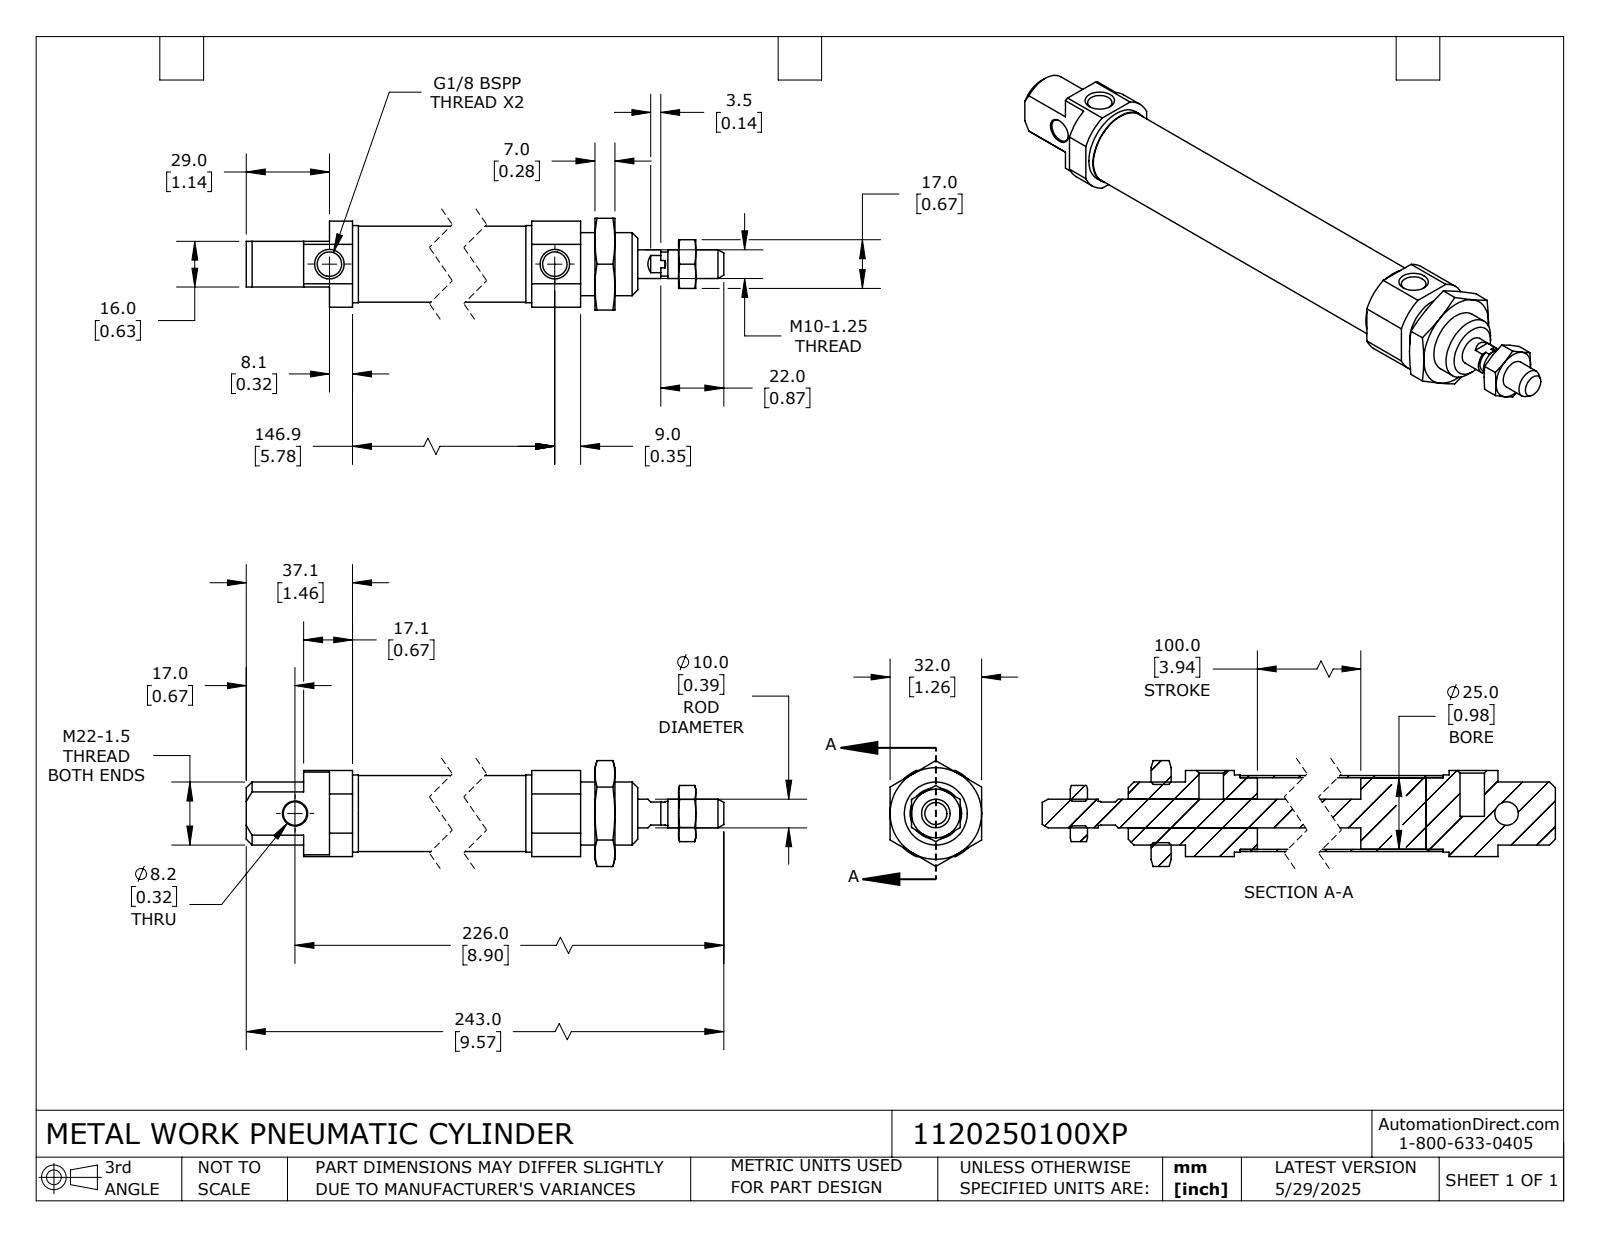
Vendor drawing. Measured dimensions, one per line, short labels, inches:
name: 1120250100XP; 1120250100XP_BODY; 1120250100XP_ROD
written by: SolidWorks 2024 (CONFIG_CONTROL_DESIGN)
unit: in
bodies: 6 solids, 144 faces (54 planar, 44 cylindrical, 46 other)
size: 9.567 × 1.455 × 1.26
volume: 4.798 in³; area: 71.12 in²
holes: 2× ⌀0.337, 1× ⌀0.323, 1× ⌀0.341, 1× ⌀0.802, 1× ⌀0.984
bosses: 1× ⌀1.063, 1× ⌀1.044, 1× ⌀0.99, 1× ⌀0.866, 1× ⌀0.394, 1× ⌀0.331
rounds: 1× R0.65
face distances: 0.276, 0.315, 1.461, 0.906, 1.181, 6.61, 5.823, 0.988, 0.63, 5.15
hole spacings: 6.102
